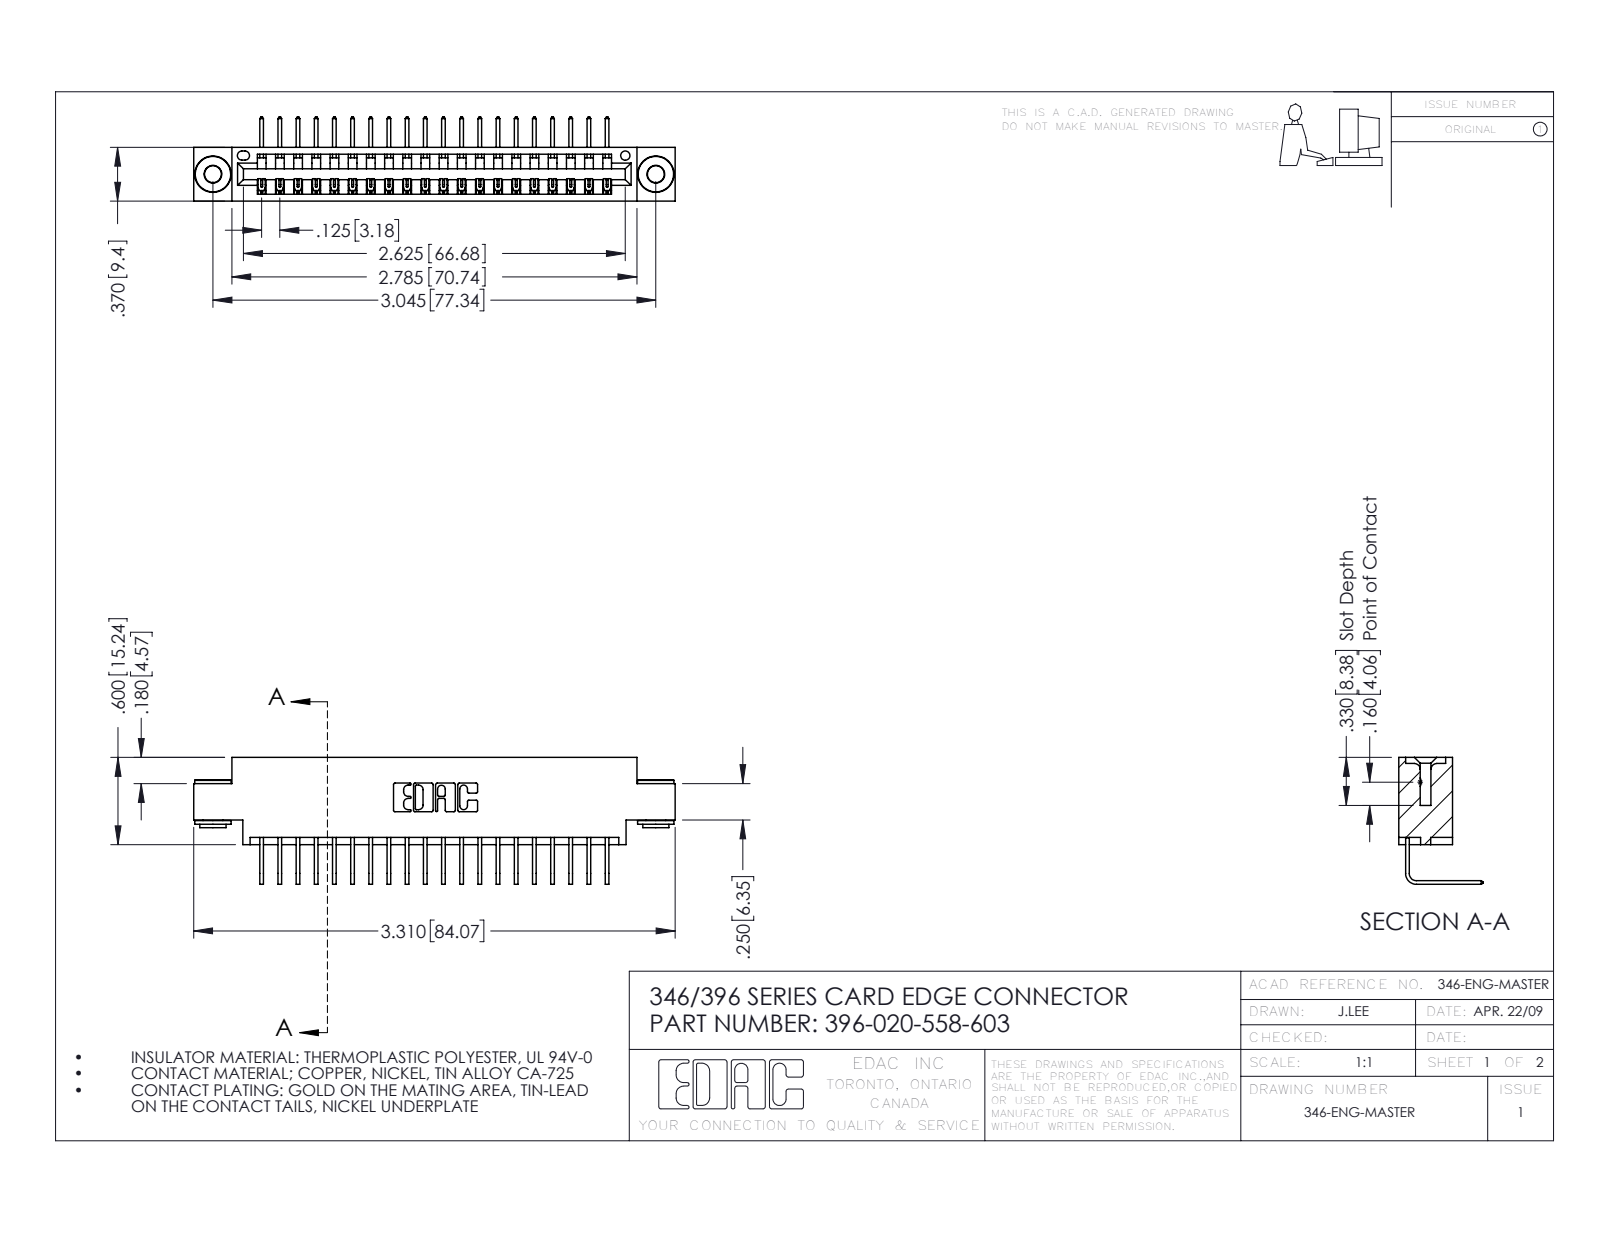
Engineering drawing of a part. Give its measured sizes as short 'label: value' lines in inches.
name: 345-250-002_345-250-002-102; 345-292-001_558 Tail - 2; 346 Part_0.170 Offset - 0.156 Dia-TH; 396-020-558-603
written by: SolidWorks 2016 (CONFIG_CONTROL_DESIGN)
unit: in
bodies: 23 solids, 1364 faces (930 planar, 426 cylindrical, 8 other)
size: 3.31 × 0.873 × 0.58
volume: 0.478 in³; area: 16 in²
holes: 2× ⌀0.116, 2× ⌀0.156, 1× ⌀0.064
bosses: 2× ⌀0.25, 2× ⌀0.18, 2× ⌀0.136
rounds: 40× R0.006, 22× R0.01, 6× R0.007, 6× R0.031, 3× R0.026, 2× R0.031, 2× R0.04, 1× R0.014
face distances: 0.322, 0.048, 0.37, 0.25, 0.025, 0.298, 0.072, 0.148, 0.222, 0.1
hole spacings: 0.246, 2.837, 3.045
